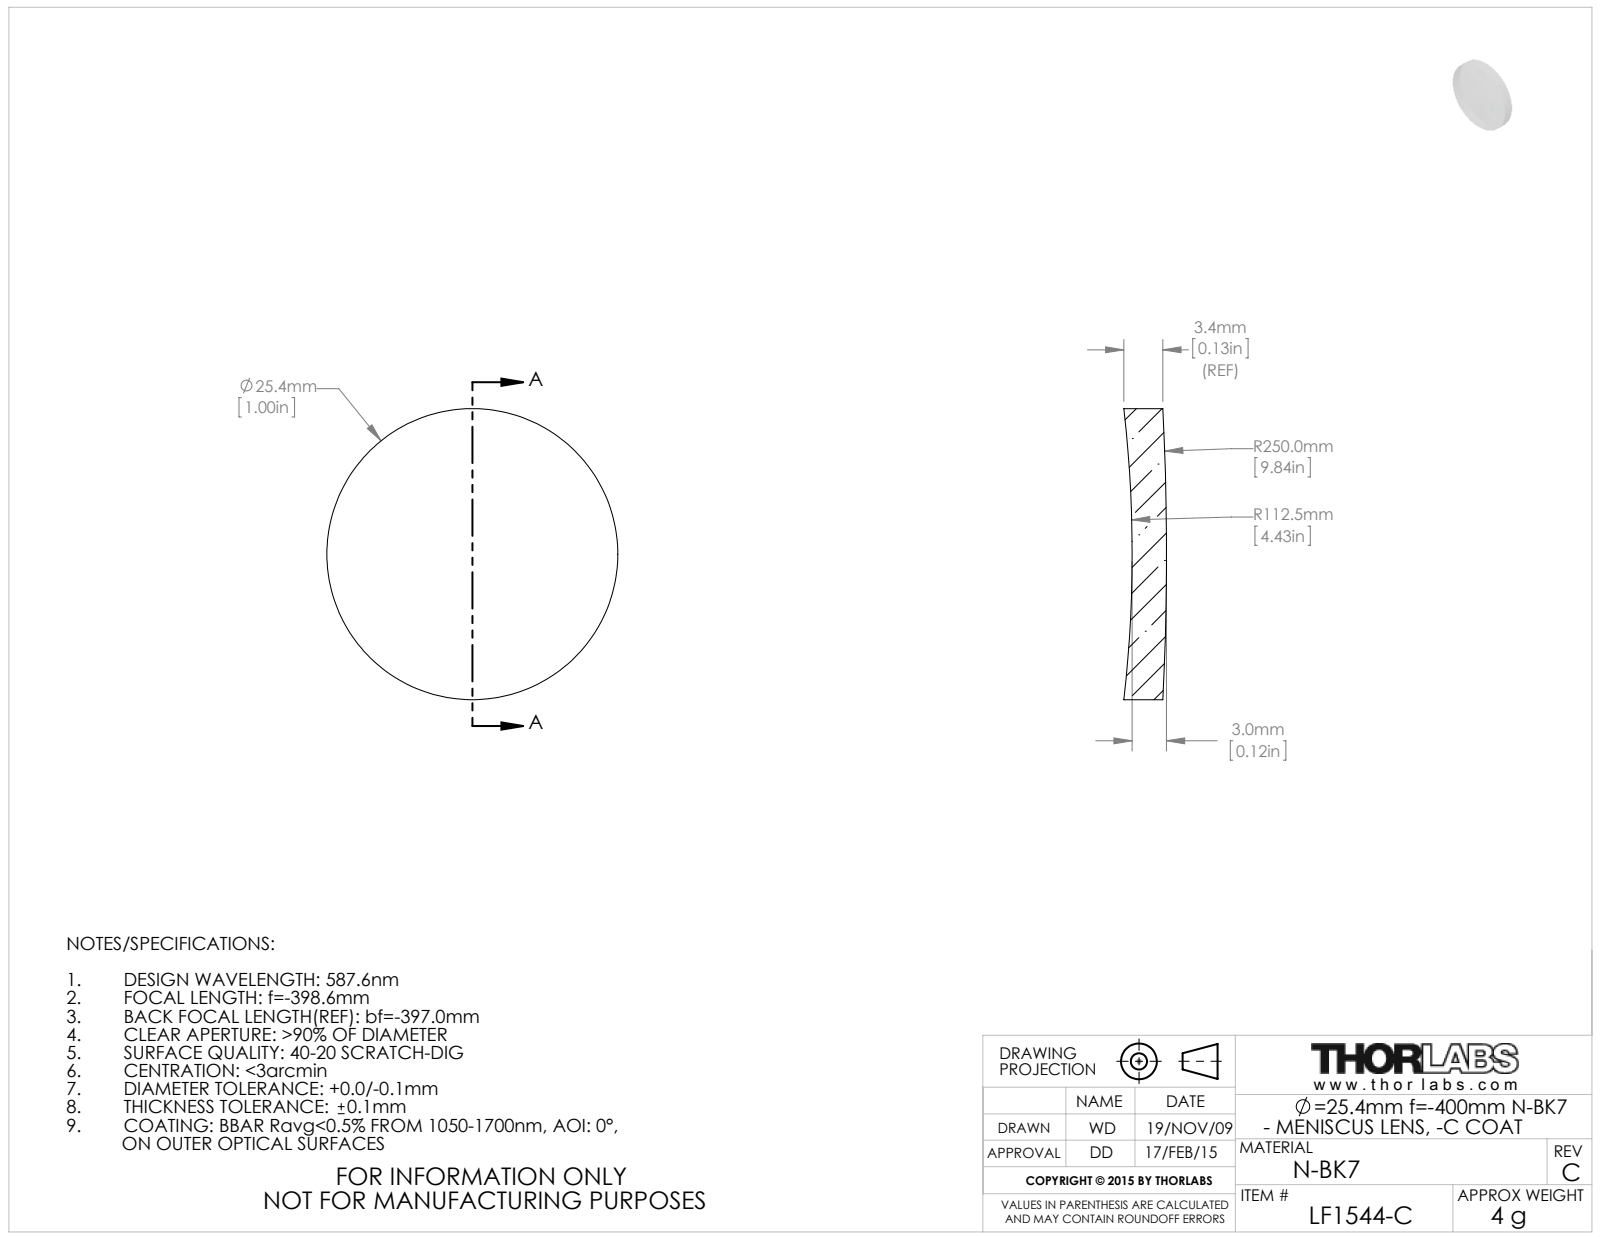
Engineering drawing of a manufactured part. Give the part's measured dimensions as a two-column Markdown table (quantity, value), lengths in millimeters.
| quantity | value |
| --- | --- |
| part name | 4911-E0W |
| STEP written by | SolidWorks 2009 (AUTOMOTIVE_DESIGN) |
| units | millimeters |
| bodies | 1 solid, 6 faces (0 planar, 2 cylindrical, 4 other) |
| overall size | 25.4 × 25.4 × 3.72 |
| volume | 1 620 mm³ |
| surface area | 1 286 mm² |
| round bosses / shafts (diameter × count) | 25.4 × 1 |
